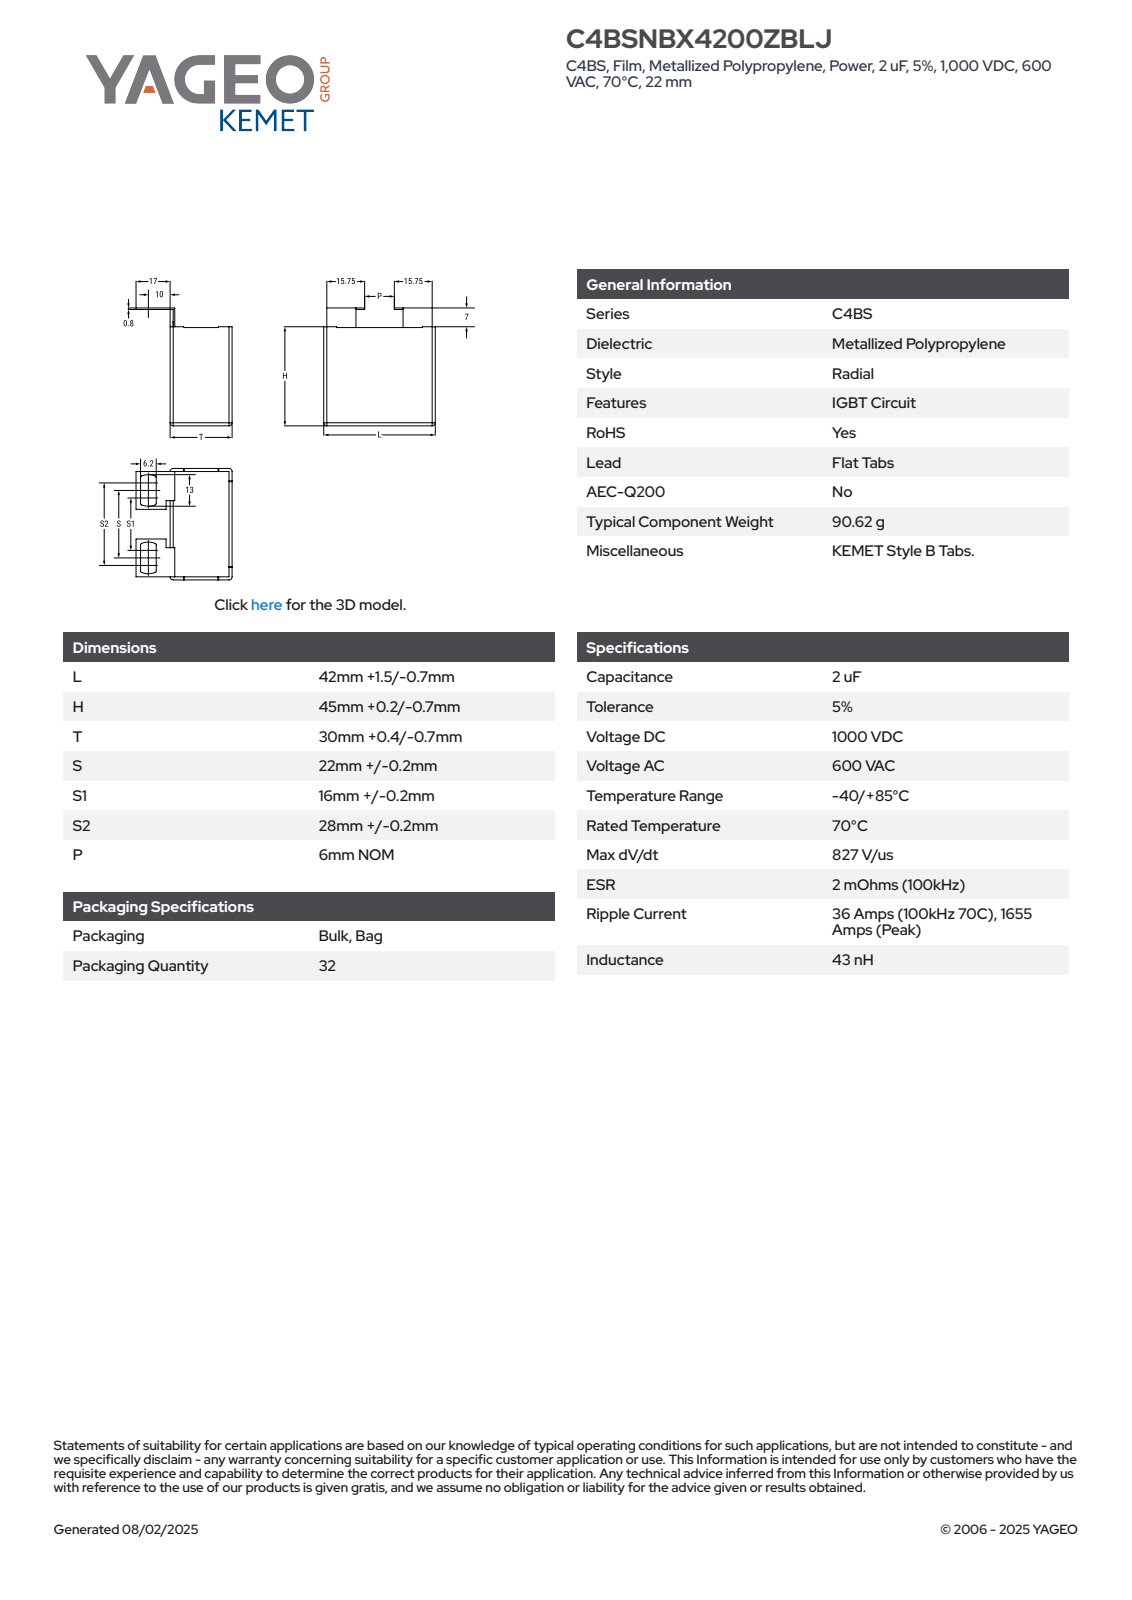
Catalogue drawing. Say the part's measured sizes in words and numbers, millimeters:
The part is named "CFP_C4BB_42X45X30_L43.5H45.2T30.4S22.2". Its 3-D file was written by "SolidWorks 2014 (AUTOMOTIVE_DESIGN)". It is 4 solids with 93 faces: 85 planar, 8 cylindrical and 0 other. Overall it measures 52.2 by 47.4 by 43.5 millimeters. Its volume is 60 307 cubic millimeters and its surface area 10 914 square millimeters. Partial cylindrical surfaces (rounded edges, fillets, slot ends): 4 of radius 4.6, 2 of radius 0.2. The main face-to-face distances are 30.4, 43.5, 45.2, 0.8, 7, 52.2, 6.2, 51.4, 28.4, 2.
